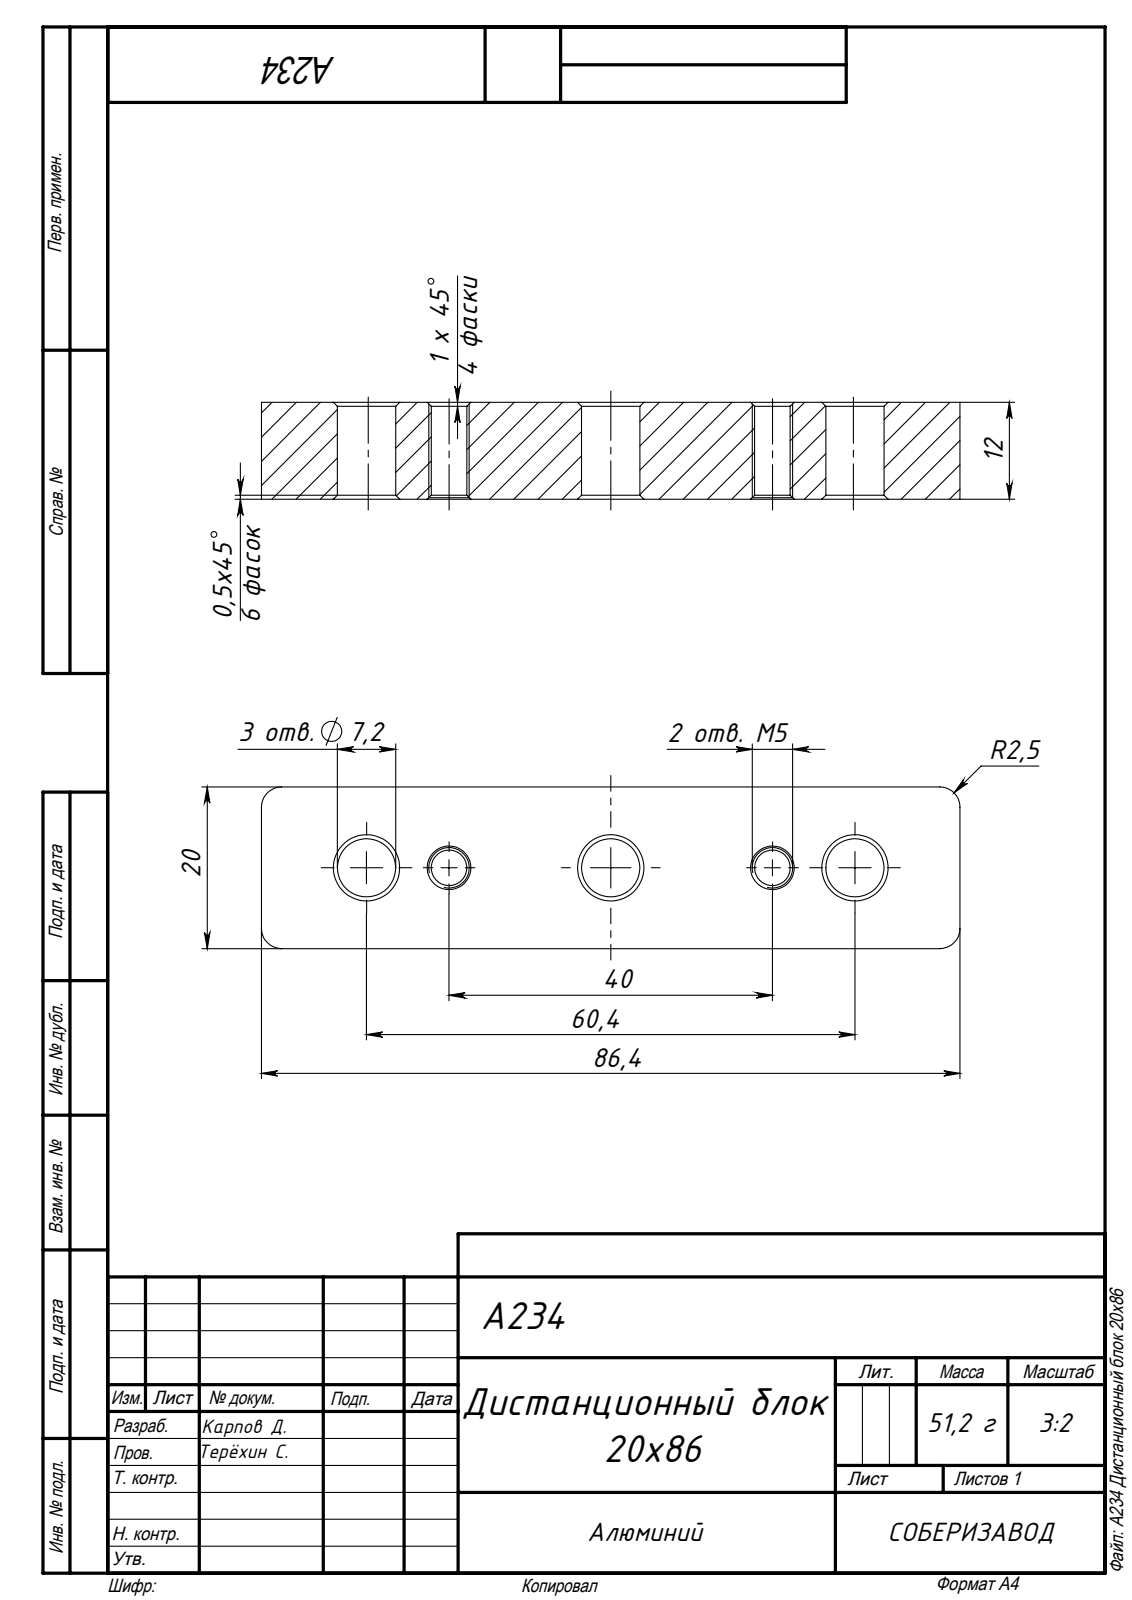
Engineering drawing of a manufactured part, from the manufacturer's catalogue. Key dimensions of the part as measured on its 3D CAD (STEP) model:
Part name (STEP PRODUCT): A234 Дистанционный блок 20х86
STEP written by: SolidWorks 2018 (AUTOMOTIVE_DESIGN)
Units: millimetres
Bodies: 1 solid, 40 faces (6 planar, 14 cylindrical, 20 other)
Overall size (bounding box): 86.4 × 20 × 12
Volume: 18 816 mm³ · Surface area: 6 736 mm²
Round holes (diameter × count): ⌀7.2 ×3, ⌀4.4 ×2
Partial cylindrical surfaces — rounded edges, fillets, slot ends (radius × count): R2.5 ×4
Main face-to-face distances: 12, 20, 86.4
Hole centre spacings: 10.2, 20, 30.2, 50.2, 40, 60.4
